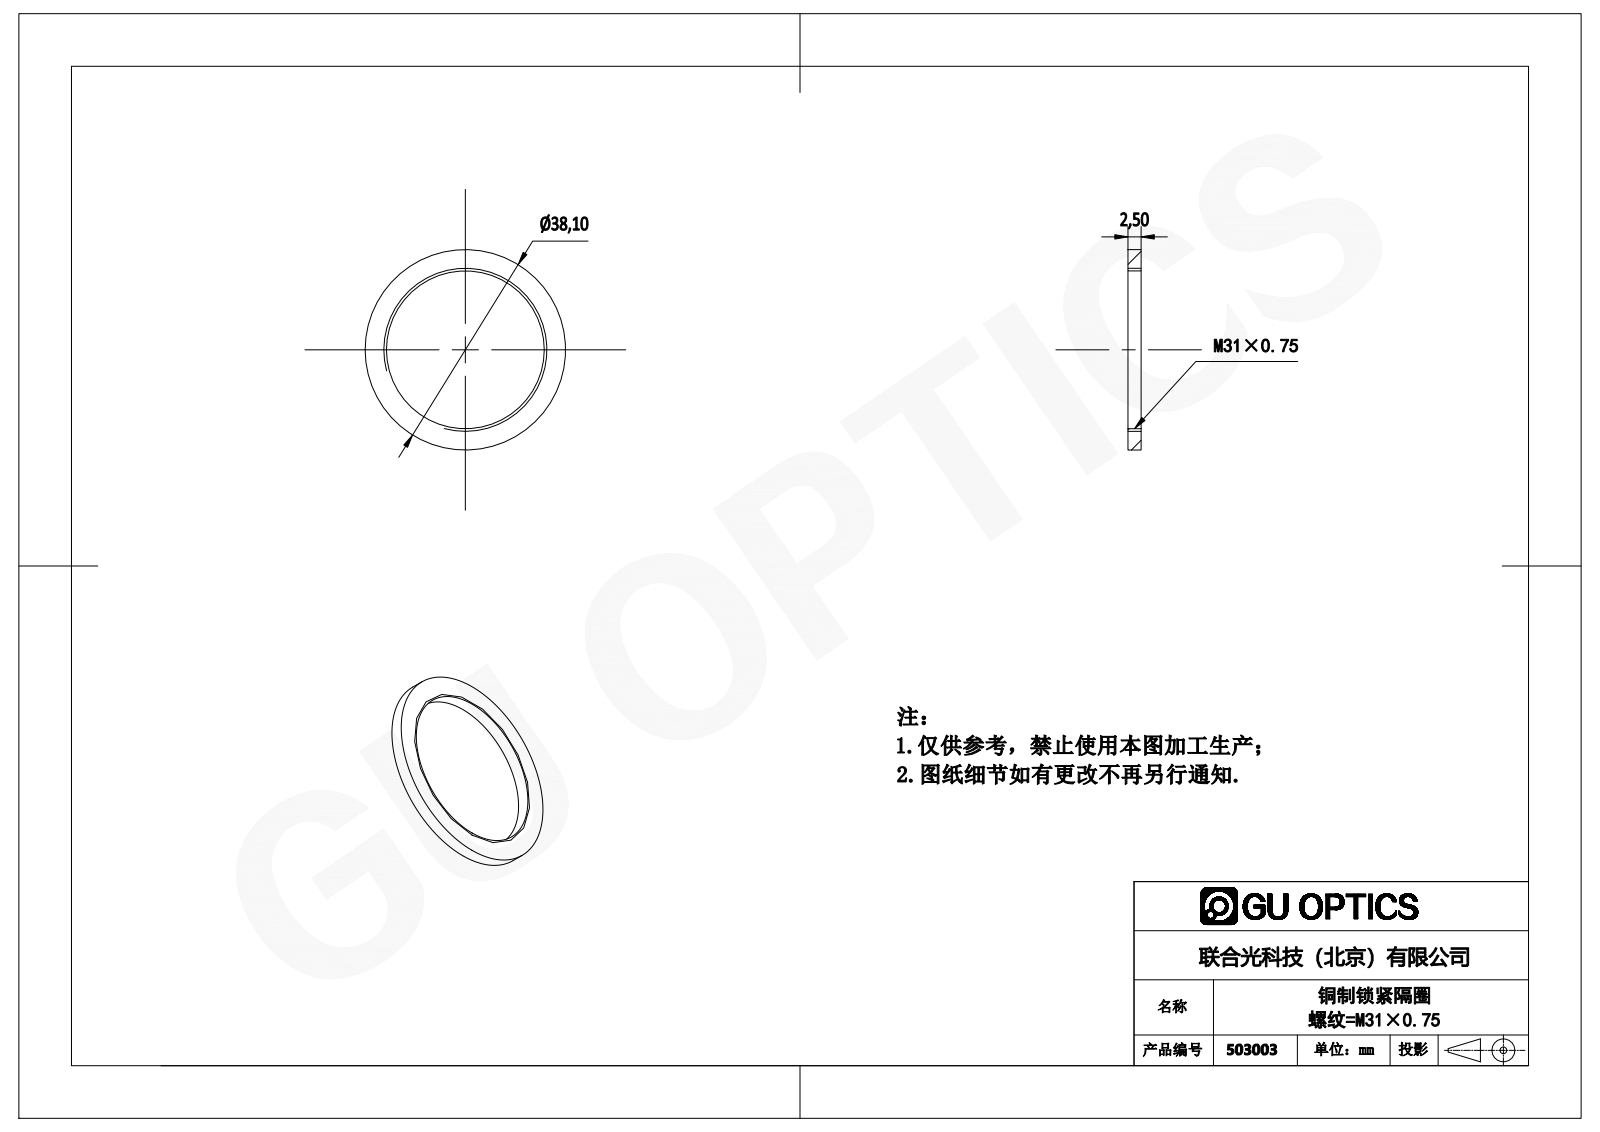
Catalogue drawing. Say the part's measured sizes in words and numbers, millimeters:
The part is named "511003". Its 3-D file was written by "SolidWorks 2016 (AUTOMOTIVE_DESIGN)". It is 1 solid with 6 faces: 2 planar, 4 cylindrical and 0 other. Overall it measures 38.1 by 38.1 by 2.5 millimeters. Its volume is 1 083 cubic millimeters and its surface area 1 401 square millimeters. Round holes: 1 of diameter 30. Round bosses or shafts: 1 of diameter 38.1. The main face-to-face distances are 2.5.
